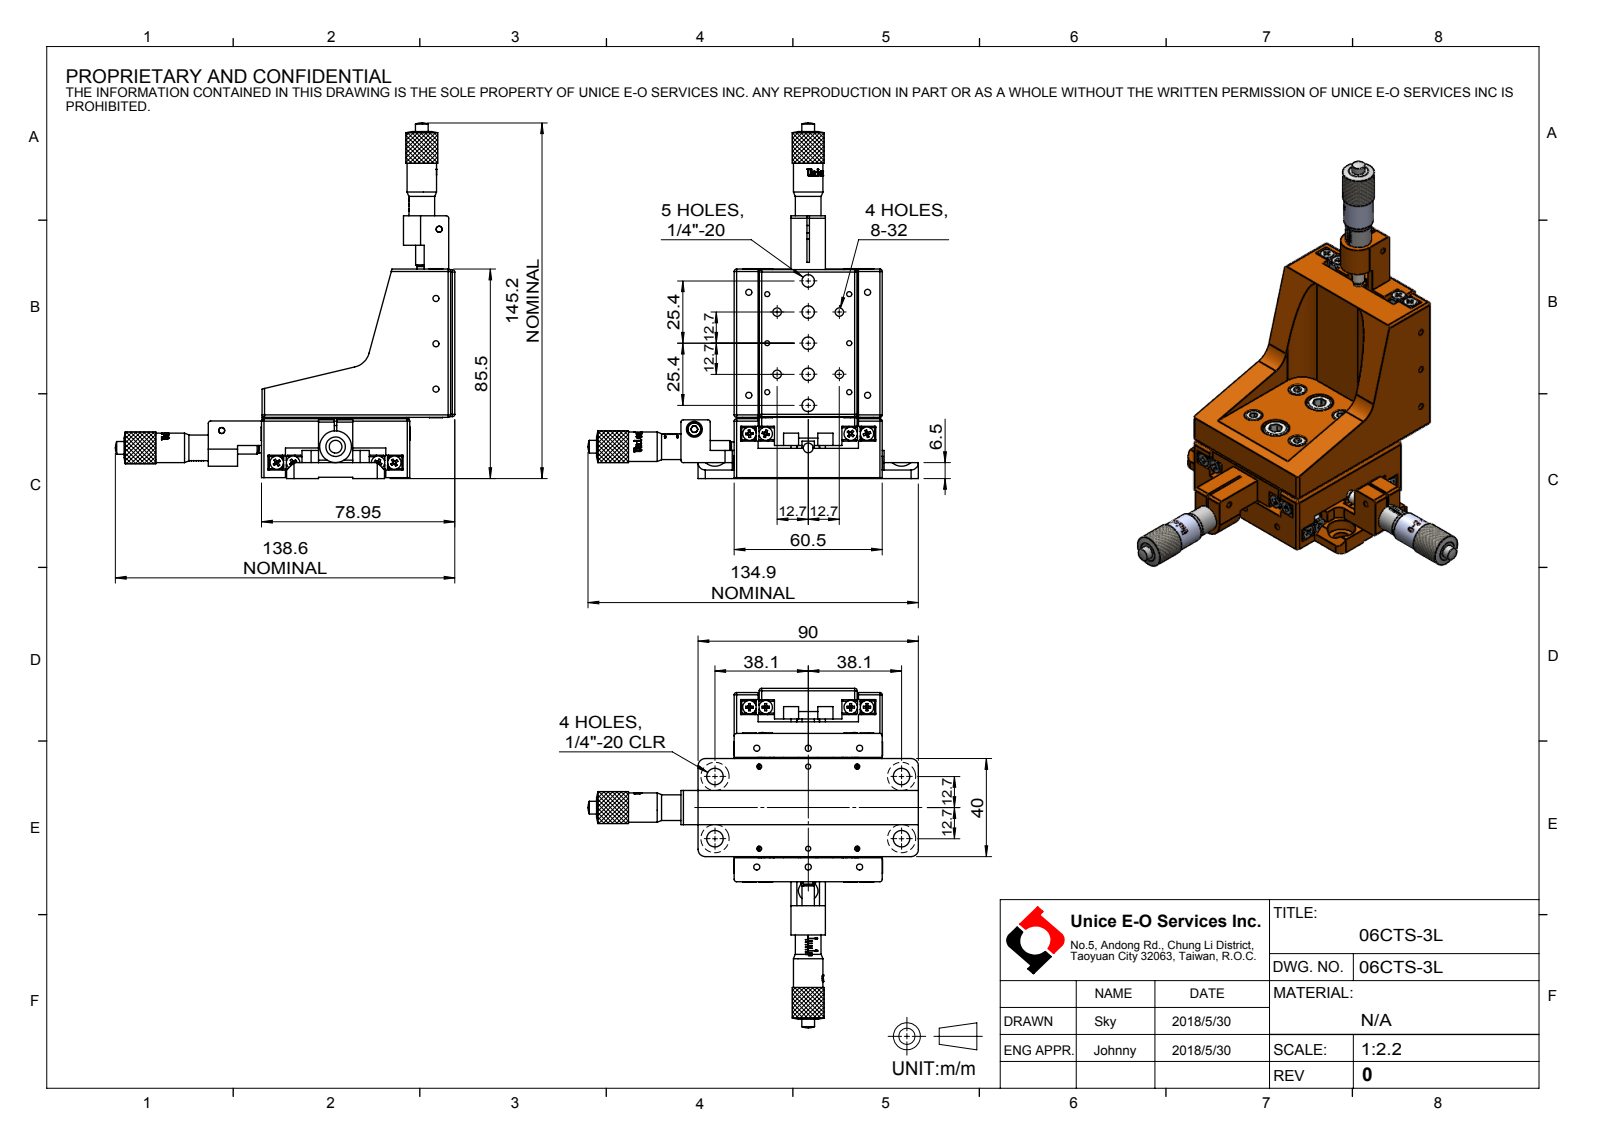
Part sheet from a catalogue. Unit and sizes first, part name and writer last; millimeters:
Units: millimetres
Overall size (bounding box): 145.15 × 138.6 × 134.9
Round holes (diameter × count): ⌀2.5 ×21, ⌀2.05 ×14, ⌀11.51 ×6, ⌀5.11 ×5, ⌀3.45 ×4, ⌀6.76 ×4, ⌀7.54 ×4, ⌀6.5 ×3, ⌀9.5 ×3, ⌀1.6 ×2, ⌀8 ×2, ⌀4 ×1
Round bosses / shafts (diameter × count): ⌀5.5 ×16, ⌀13 ×3, ⌀12 ×3, ⌀10.5 ×3, ⌀9.2 ×3, ⌀7 ×3, ⌀5.2 ×3, ⌀5 ×3
Partial cylindrical surfaces — rounded edges, fillets, slot ends (radius × count): R1 ×38, R3 ×6, R1.5 ×3, R5.98 ×3, R2 ×2, R7 ×2, R8.5 ×2, R8 ×1
Main face-to-face distances: 3, 6, 9, 16.5, 60.5, 12.5, 3.1, 12, 11.8, 6.75
Hole centre spacings: 25.4, 12.7, 8.35, 13.33, 17.96, 20, 28.4, 30.34
Bodies: 0 solids, 1295 faces (789 planar, 350 cylindrical, 156 other)
Part name (STEP PRODUCT): 06CTS-3L
STEP written by: SolidWorks 2016 (AUTOMOTIVE_DESIGN)
